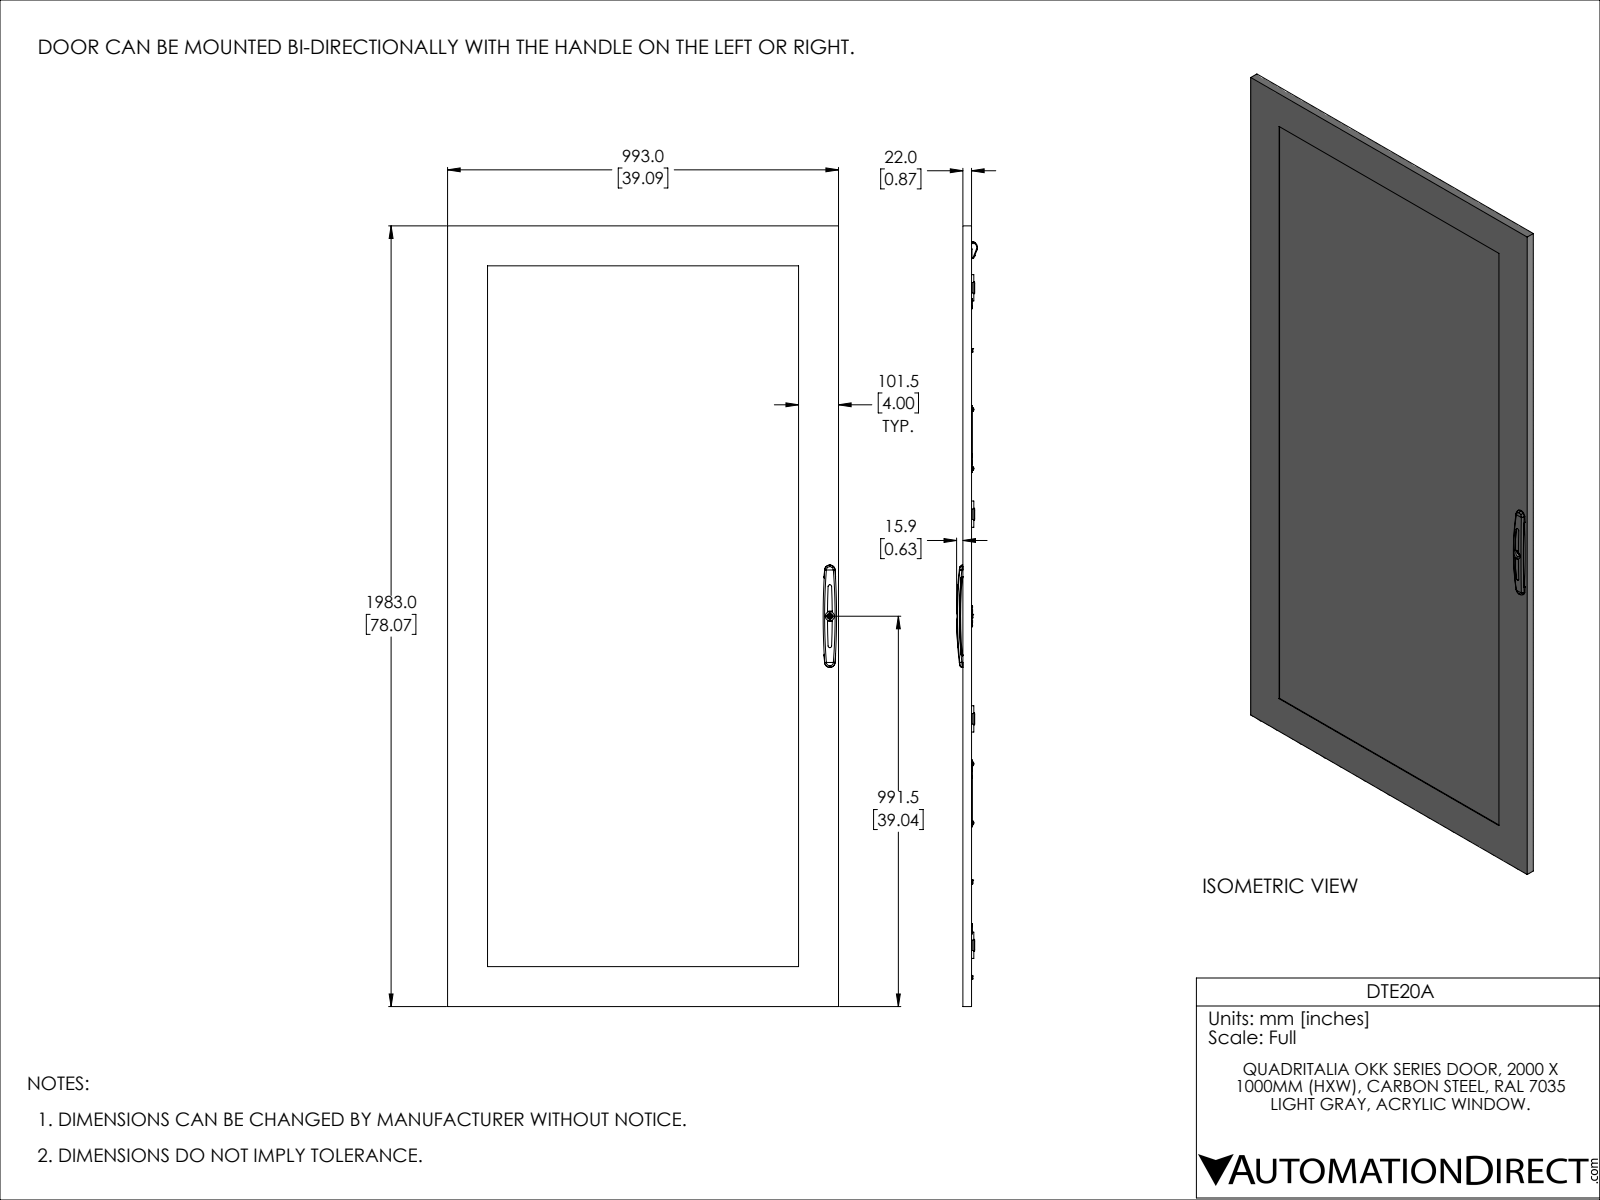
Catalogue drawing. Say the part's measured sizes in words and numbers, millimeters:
The part is named "DTE20A". Its 3-D file was written by "SolidWorks 2021 (CONFIG_CONTROL_DESIGN)". It is 102 solids with 3653 faces: 1763 planar, 1261 cylindrical and 629 other. Overall it measures 1983 by 993 by 53.1 millimeters. Its volume is 8 836 000 cubic millimeters and its surface area 5 738 000 square millimeters. Round holes: 160 of diameter 4.2, 29 of diameter 8, 20 of diameter 9, 8 of diameter 0.3, 8 of diameter 4.9, 8 of diameter 5, 6 of diameter 4.9, 4 of diameter 6.2, 4 of diameter 7, 3 of diameter 5.2, 2 of diameter 3.4, 2 of diameter 4.3. Round bosses or shafts: 21 of diameter 7, 17 of diameter 6, 14 of diameter 7.2, 10 of diameter 10, 9 of diameter 5, 8 of diameter 4.9, 2 of diameter 12, 2 of diameter 8. Partial cylindrical surfaces (rounded edges, fillets, slot ends): 74 of radius 0.3, 70 of radius 1, 36 of radius 1.5, 33 of radius 0.5, 28 of radius 2.5, 16 of radius 4.5, 15 of radius 2, 14 of radius 5.8. The main face-to-face distances are 4, 2, 6, 1.5, 18.5, 20, 17, 22, 860, 16. The hole center spacings are 25, 50, 75, 100, 125, 150, 175, 200.
